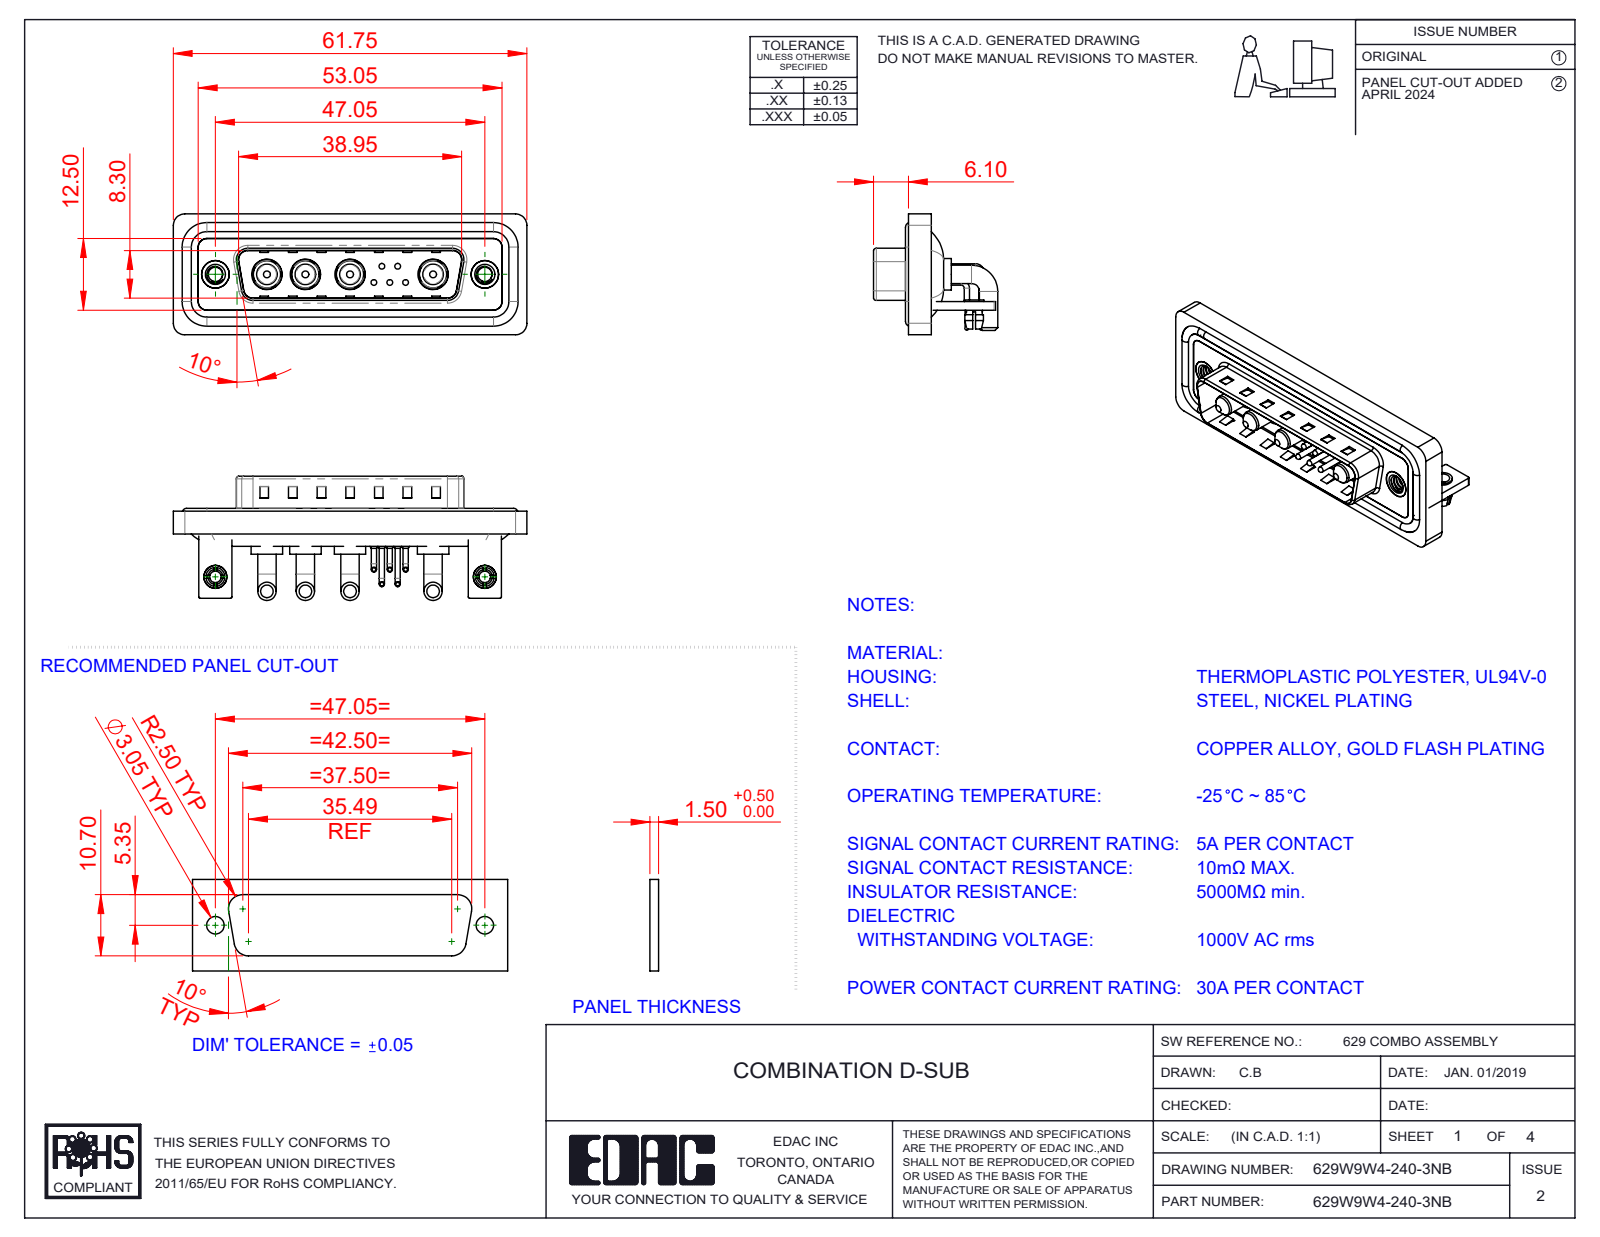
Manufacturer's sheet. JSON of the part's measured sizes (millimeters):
{"part_name": "629Combo Shell Front_25 Contacts; 629Combo Contact Row 2; 629Combo Waterproof Housing_25 Contacts; 629Combo Shell Rear_25 Contacts (+7 more)", "step_written_by": "SolidWorks 2023 (CONFIG_CONTROL_DESIGN)", "units": "millimeters", "bodies": {"solids": 24, "faces": 1335, "planar": 637, "cylindrical": 502, "other": 196}, "overall_size": [61.75, 21.7, 21.1], "volume_mm3": 8125, "surface_area_mm2": 13249, "round_holes": [[2, 7], [0.75, 5], [1.6, 5], [2.5, 4], [4.85, 4], [5.3, 4], [3.2, 2], [4, 2], [4.8, 2], [5, 2]], "round_bosses_or_shafts": [[0.9, 10], [3.2, 8], [1.5, 5], [1, 5], [0.65, 5], [5.5, 4], [5.2, 4], [4.75, 4]], "partial_cylinders_radius": [[2, 19], [1.5, 18], [0.25, 16], [0.5, 9], [1.6, 8], [1.01, 5], [0.6, 4], [0.65, 4]], "face_to_face_distances": [0.4, 1.5, 0.8, 2.9, 2.1, 1.1, 3.7, 4.1, 4.5, 1.6], "hole_center_spacings": [3.16, 2.77, 5.04, 14.5, 47.05, 2.78, 4.4, 4.41]}
